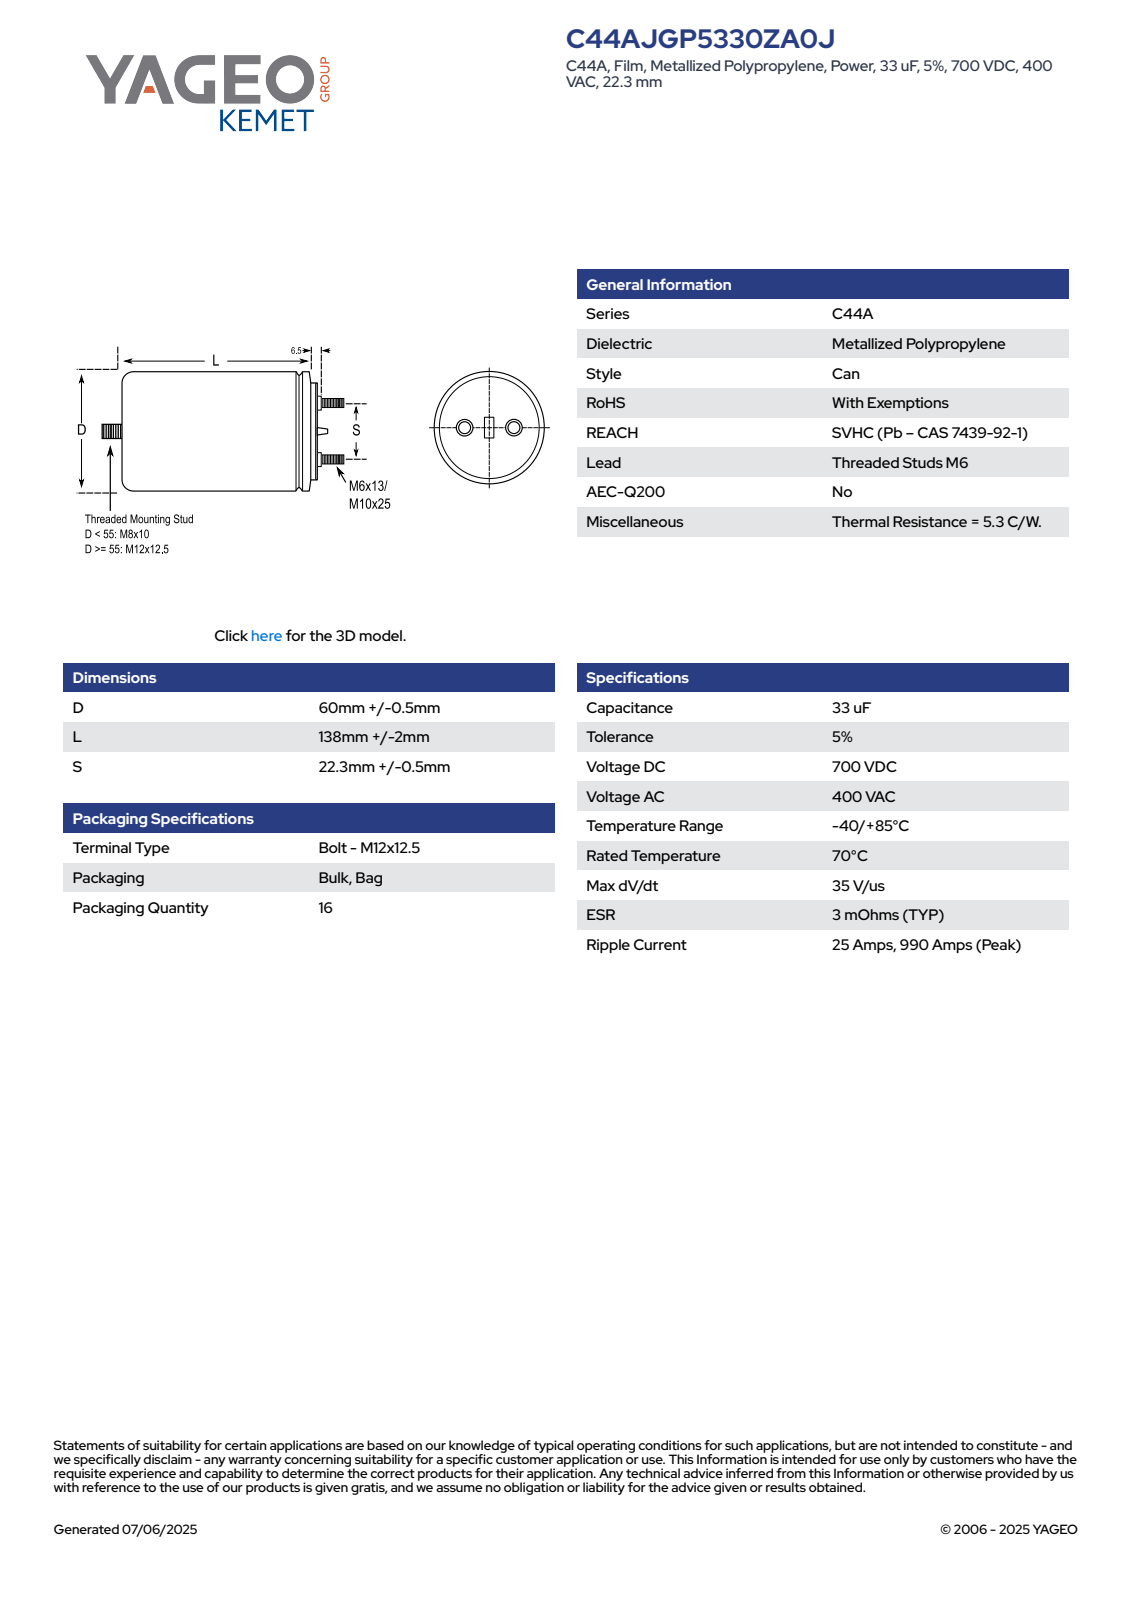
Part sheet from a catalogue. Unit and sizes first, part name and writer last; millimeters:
Units: millimetres
Overall size (bounding box): 172 × 60.5 × 60.5
Round bosses / shafts (diameter × count): ⌀9 ×2, ⌀6 ×2, ⌀60.5 ×1, ⌀47.45 ×1, ⌀12 ×1
Partial cylindrical surfaces — rounded edges, fillets, slot ends (radius × count): R30.24 ×1
Main face-to-face distances: 145, 12.5, 157.5, 159, 146.5, 1.5, 172, 159.5, 14.5, 13
Volume: 410 307 mm³ · Surface area: 33 718 mm²
Bodies: 1 solid, 102 faces (29 planar, 34 cylindrical, 39 other)
Part name (STEP PRODUCT): CFP_C44A_60X138_D60.5L140S22.3
STEP written by: SolidWorks 2014 (AUTOMOTIVE_DESIGN)
